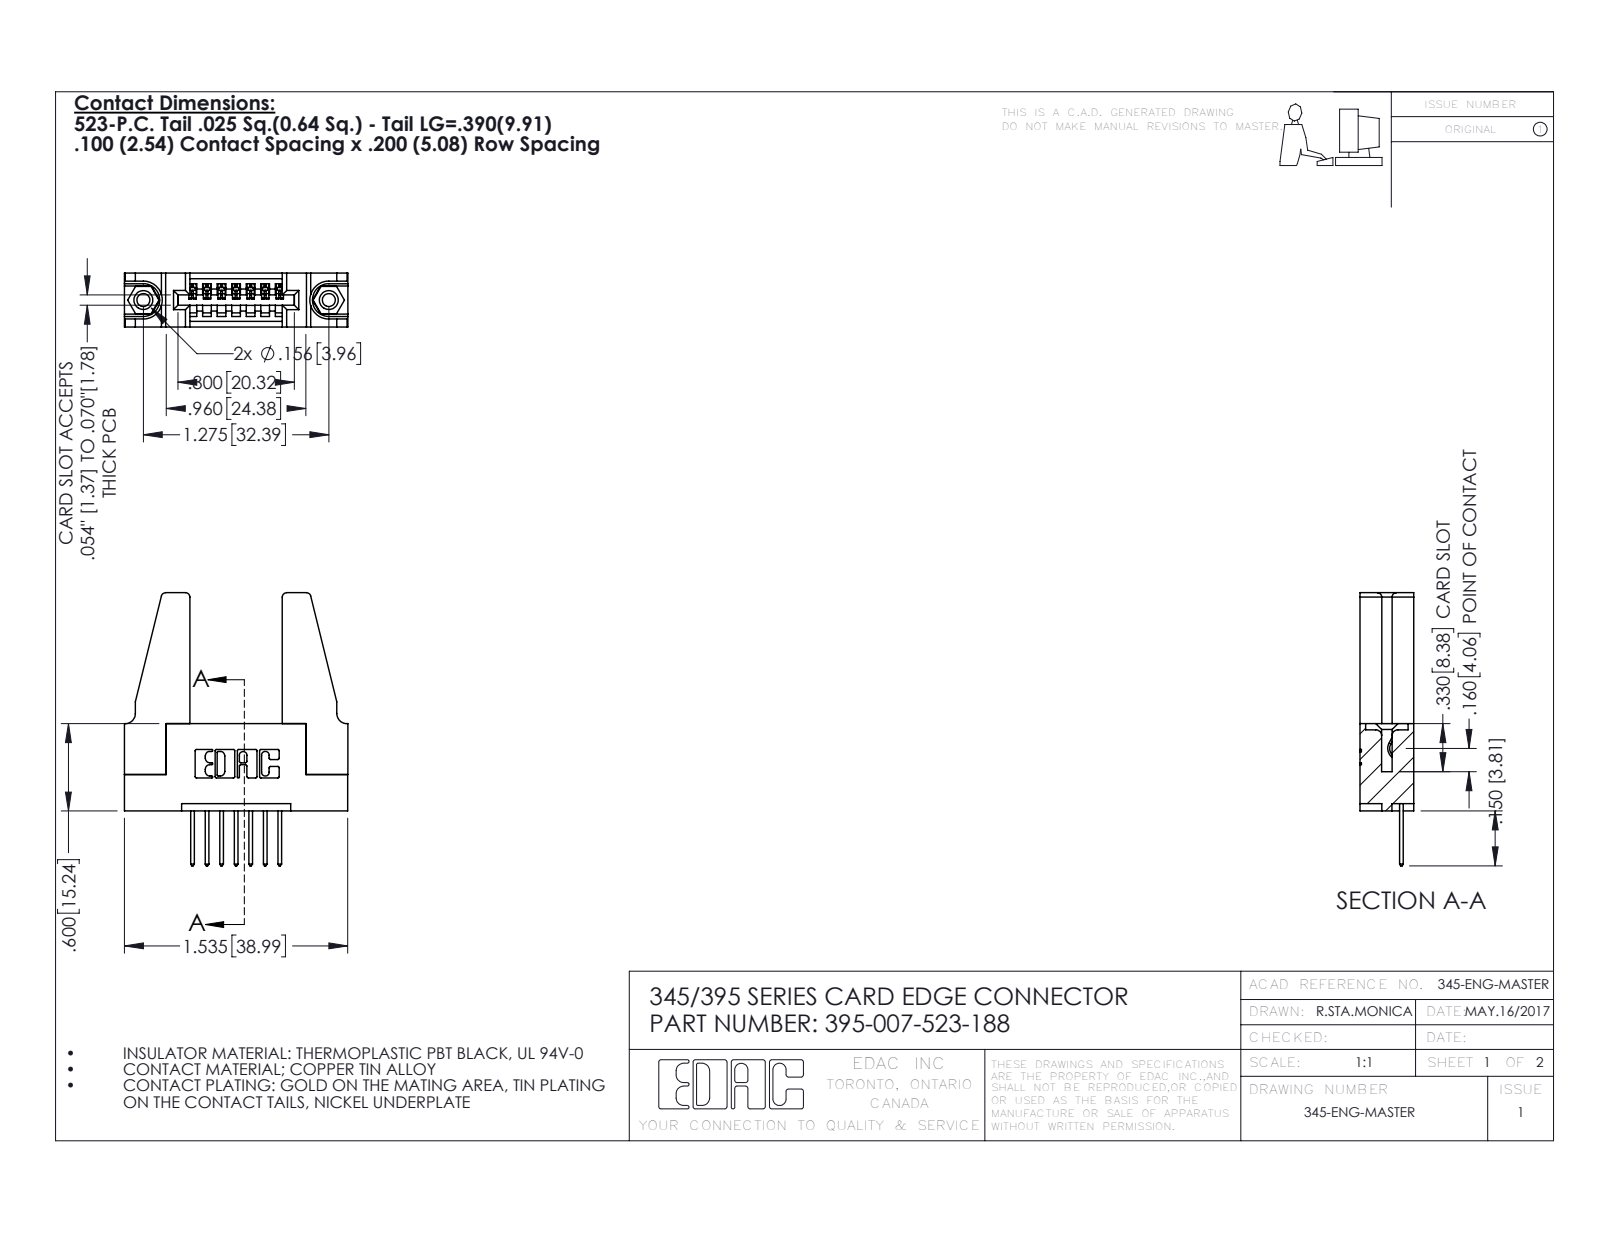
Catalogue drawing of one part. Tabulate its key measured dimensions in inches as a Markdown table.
| quantity | value |
| --- | --- |
| part name | 345-220-078_345-220-088; 345-250-001_345-250-001-102; 345 Part_Flush Mounting Lugs - 0.156 Dia-TH; 345-292-001_345-293-123 (+1 more) |
| STEP written by | SolidWorks 2016 (CONFIG_CONTROL_DESIGN) |
| units | inches |
| bodies | 12 solids, 656 faces (432 planar, 208 cylindrical, 16 other) |
| overall size | 1.877 × 1.536 × 0.37 |
| volume | 0.407 in³ |
| surface area | 11.16 in² |
| round holes (diameter × count) | 0.089 × 2, 0.125 × 2, 0.156 × 2, 0.064 × 1 |
| round bosses / shafts (diameter × count) | 0.155 × 2 |
| partial cylindrical surfaces (radius × count) | 0.01 × 22, 0.006 × 14, 0.01 × 14, 0.03 × 8, 0.007 × 6, 0.031 × 6, 0.026 × 3, 0.031 × 2 |
| main face-to-face distances | 0.37, 0.072, 0.298, 0.2, 0.098, 0.272, 0.025, 0.148, 0.15, 0.25 |
| hole center spacings | 0.27, 1.045, 1.275 |
